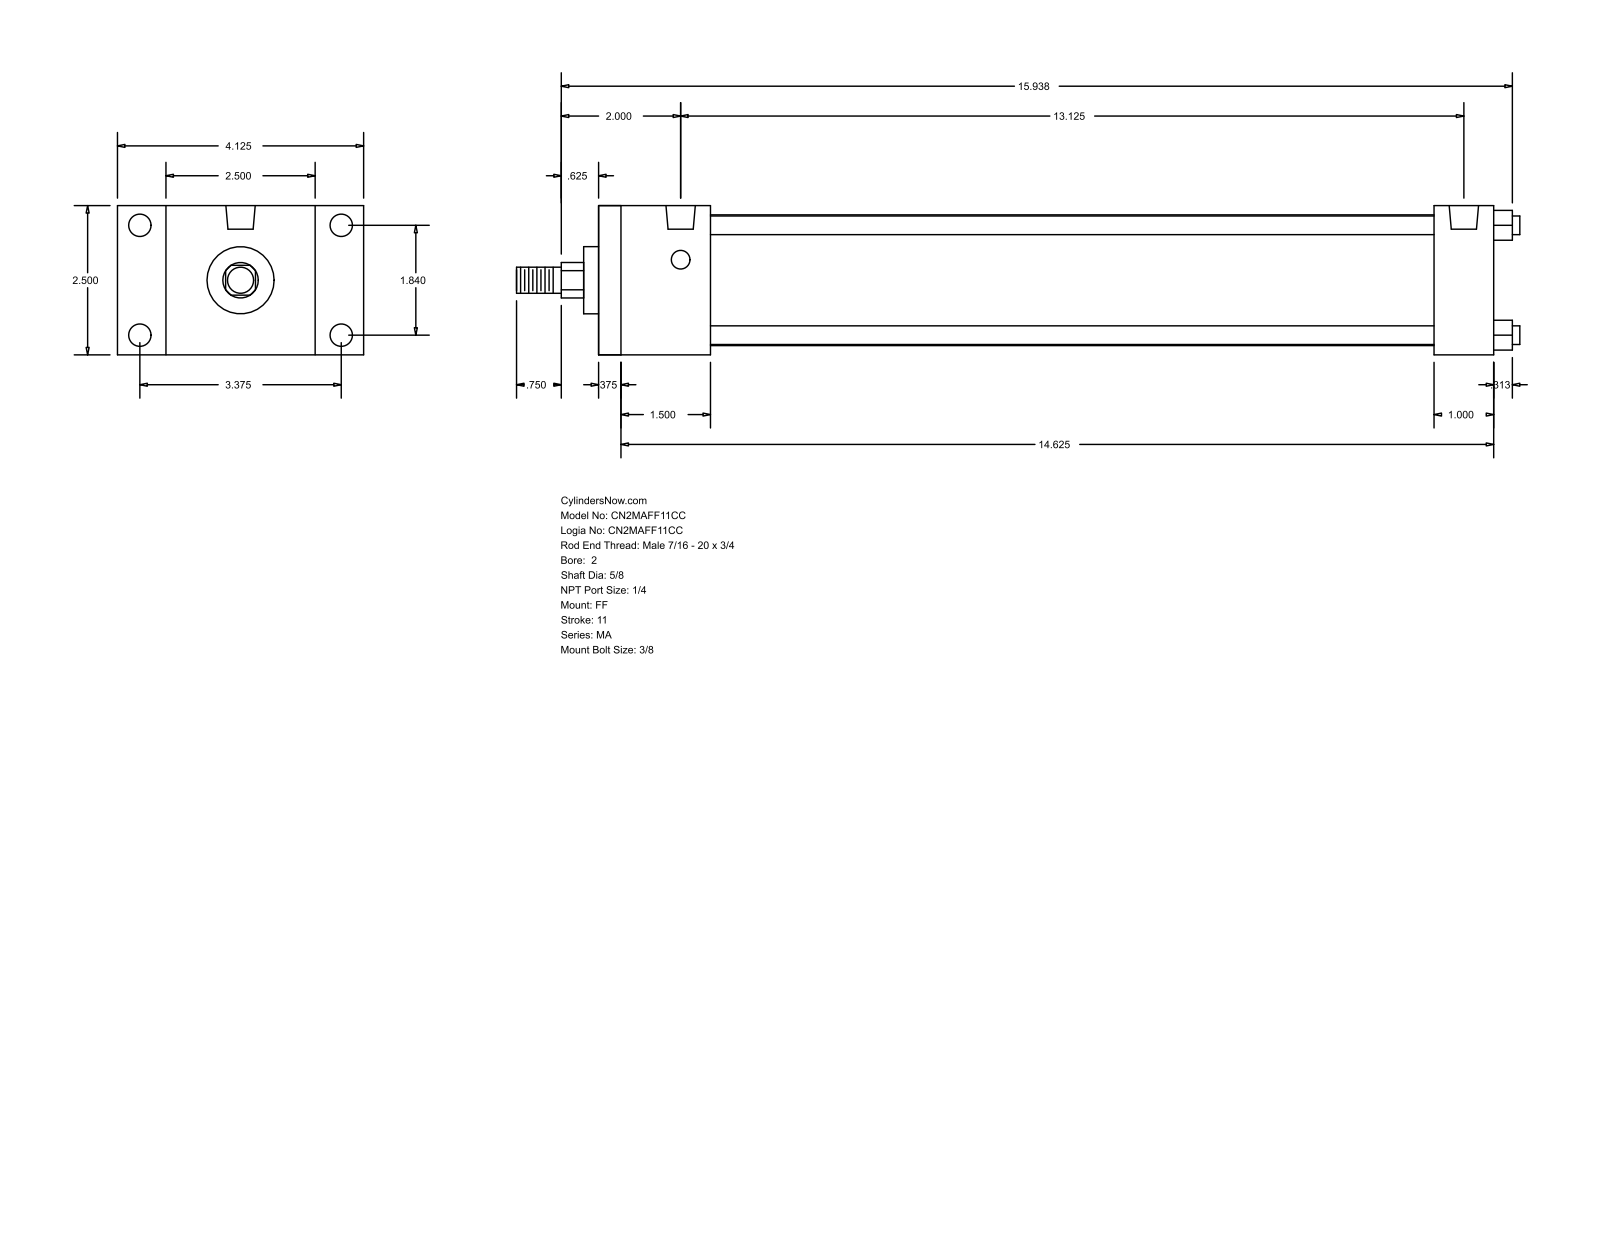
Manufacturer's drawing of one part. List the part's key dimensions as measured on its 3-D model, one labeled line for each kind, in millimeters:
Part name (STEP PRODUCT): MA_FF__0200_0.625
STEP written by: GSSL Pune (CONFIG_CONTROL_DESIGN)
Units: millimetres
Bodies: 0 solids, 92 faces (64 planar, 28 cylindrical, 0 other)
Overall size (bounding box): 427.04 × 104.78 × 63.5
Round holes (diameter × count): ⌀7.94 ×4, ⌀9.53 ×4, ⌀12.49 ×2
Round bosses / shafts (diameter × count): ⌀7.94 ×4, ⌀55.63 ×1, ⌀28.57 ×1, ⌀15.88 ×1, ⌀11.11 ×1
Partial cylindrical surfaces — rounded edges, fillets, slot ends (radius × count): R7.54 ×1
Main face-to-face distances: 63.5, 381, 371.48, 9.52, 25.4, 38.1, 47.62, 355.6, 346.08, 307.98
Hole centre spacings: 46.74, 85.72, 97.63, 333.38
